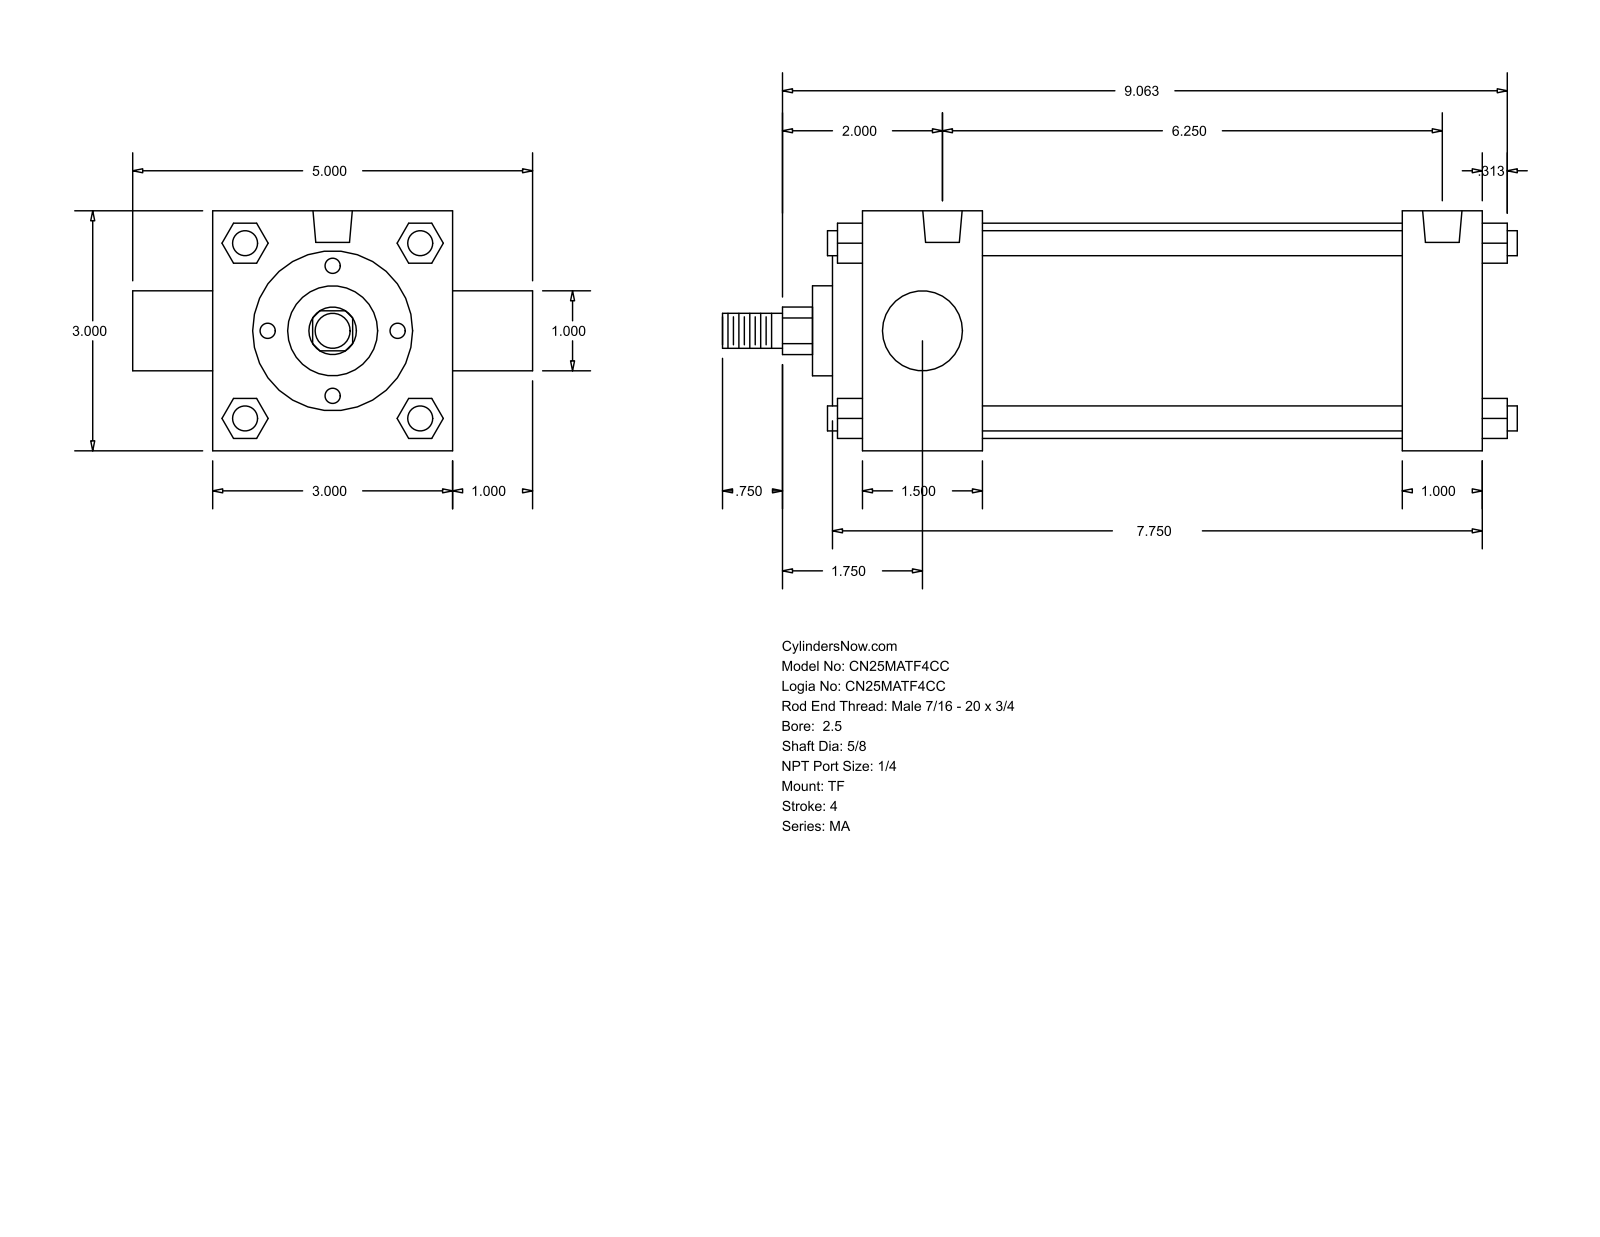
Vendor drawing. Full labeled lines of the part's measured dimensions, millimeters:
Part name (STEP PRODUCT): MA_TF__0250_0.625
STEP written by: GSSL Pune (CONFIG_CONTROL_DESIGN)
Units: millimetres
Bodies: 0 solids, 122 faces (93 planar, 29 cylindrical, 0 other)
Overall size (bounding box): 252.41 × 127 × 76.2
Round holes (diameter × count): ⌀7.94 ×3, ⌀12.49 ×2
Round bosses / shafts (diameter × count): ⌀7.94 ×4, ⌀68.33 ×1, ⌀50.8 ×1, ⌀28.57 ×1, ⌀25.4 ×1, ⌀15.88 ×1, ⌀11.11 ×1
Partial cylindrical surfaces — rounded edges, fillets, slot ends (radius × count): R7.54 ×1
Main face-to-face distances: 76.2, 196.85, 25.4, 38.1, 171.45, 133.35, 158.75, 12.7, 9.52, 47.62
Hole centre spacings: 158.75
